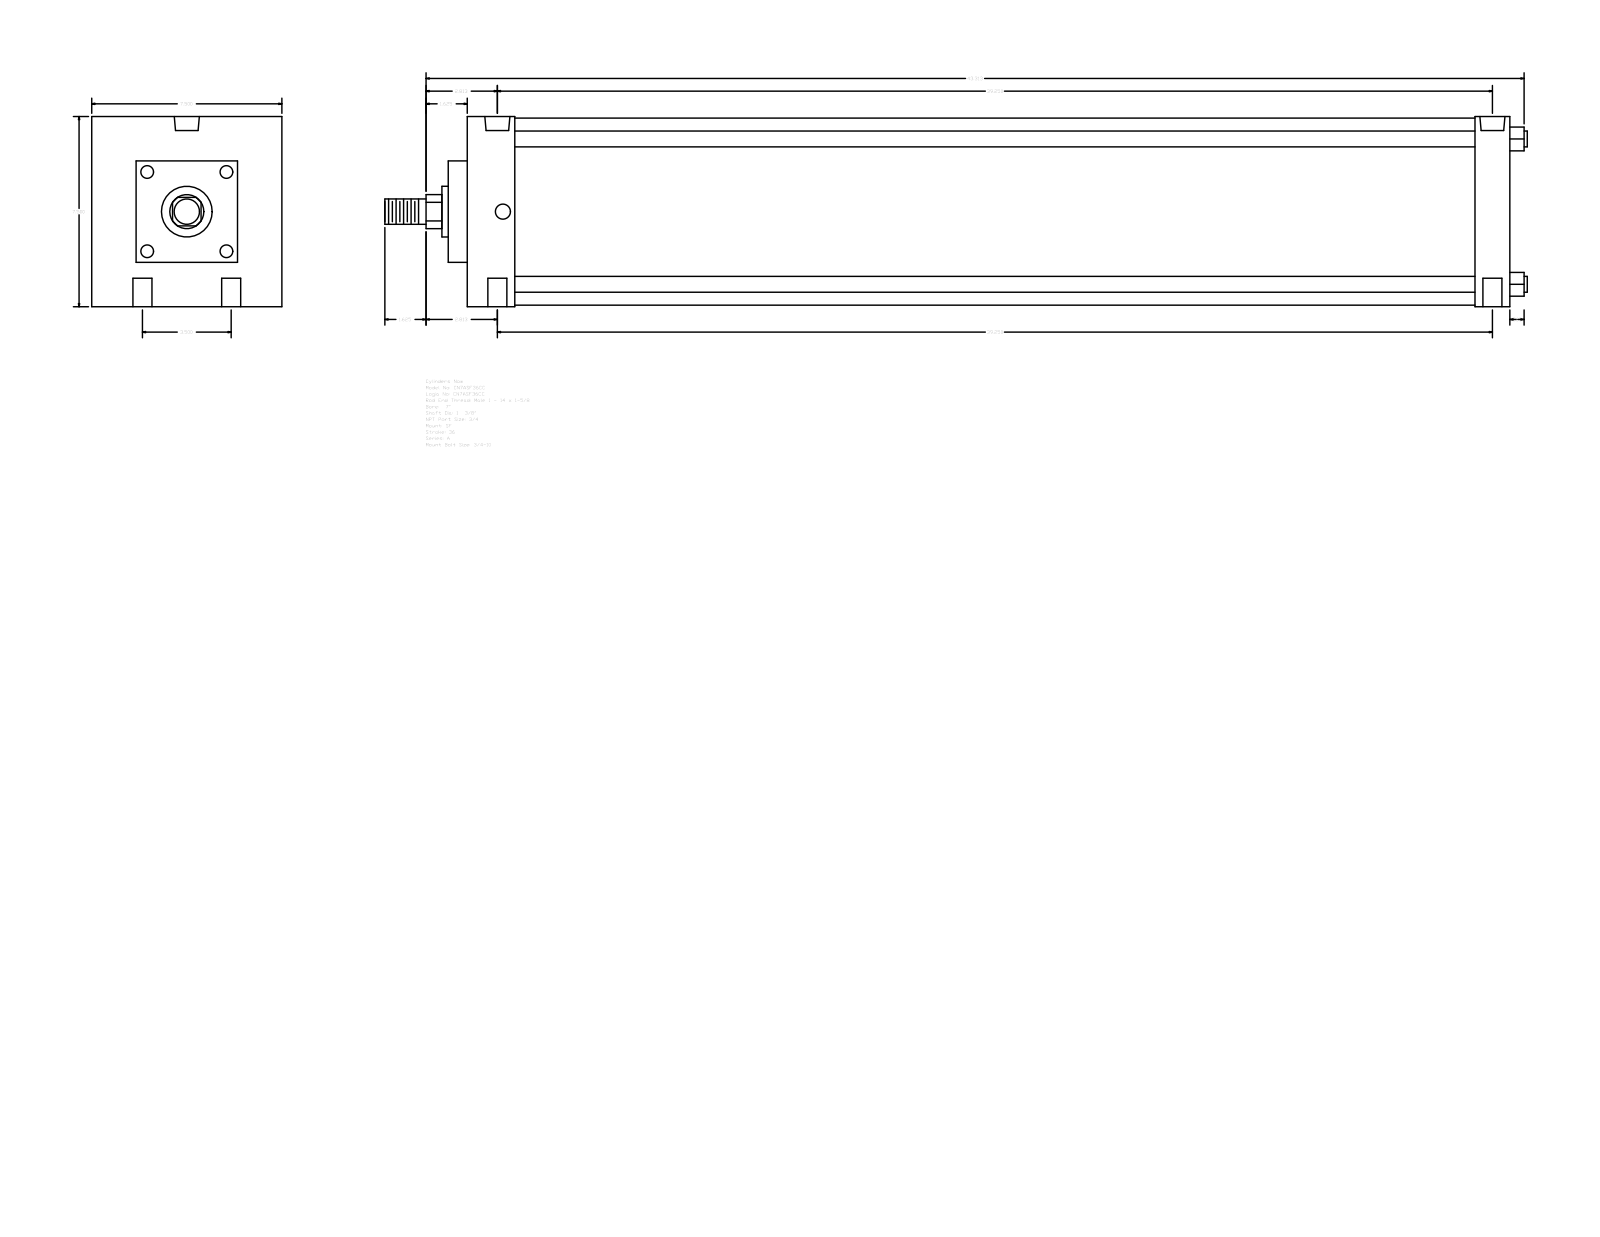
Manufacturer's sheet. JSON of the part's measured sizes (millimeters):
{"part_name": "A_SF__0700_1.375", "step_written_by": "GSSL Pune (CONFIG_CONTROL_DESIGN)", "units": "millimeters", "bodies": {"solids": 0, "faces": 93, "planar": 67, "cylindrical": 26, "other": 0}, "overall_size": [1144.59, 190.5, 190.5], "round_holes": [[19.05, 4], [15.08, 2], [25.12, 2]], "round_bosses_or_shafts": [[15.88, 4], [187.32, 1], [50.8, 1], [34.92, 1], [25.4, 1]], "partial_cylinders_radius": [[17.06, 1]], "face_to_face_distances": [190.5, 1044.58, 19.04, 1063.62, 66.67, 1028.69, 47.63, 1009.65, 962.02, 996.95], "hole_center_spacings": [44.45, 997.94, 996.95, 88.9, 1000.91, 985.83]}
